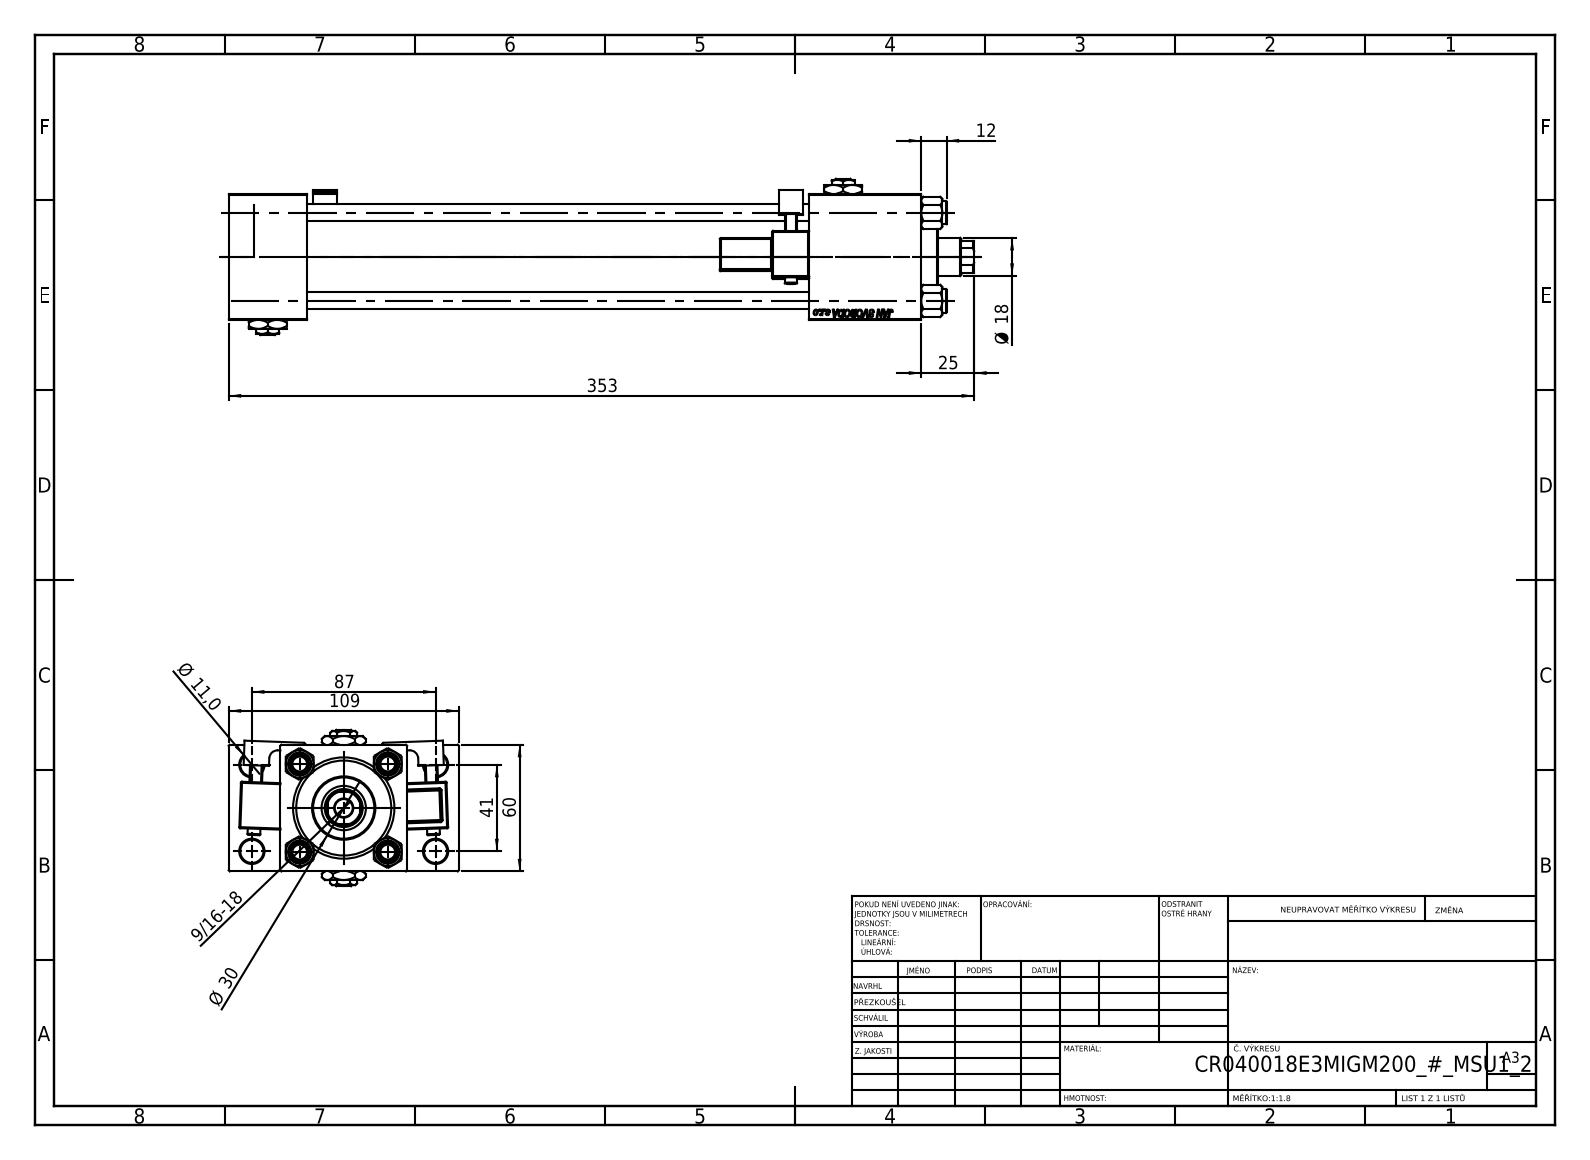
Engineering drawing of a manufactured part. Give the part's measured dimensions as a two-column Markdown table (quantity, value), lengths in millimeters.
| quantity | value |
| --- | --- |
| part name | V215CR_MSU; Zatka_pro_OIL_PORT; V215CR_E_Body; V215CR_VCP_E (+3 more) |
| STEP written by | SolidWorks 2019 (CONFIG_CONTROL_DESIGN) |
| units | millimeters |
| bodies | 15 solids, 1385 faces (602 planar, 153 cylindrical, 630 other) |
| overall size | 353 × 109 × 74 |
| volume | 695 320 mm³ |
| surface area | 216 006 mm² |
| round holes (diameter × count) | 8 × 4, 11 × 4, 7 × 3, 16.66 × 3, 24 × 3, 8.5 × 1, 18 × 1, 21 × 1, 31 × 1, 40 × 1, 45 × 1 |
| round bosses / shafts (diameter × count) | 11 × 4, 6 × 2, 46 × 1, 30 × 1 |
| partial cylindrical surfaces (radius × count) | 0.5 × 48, 1 × 2, 2.5 × 2, 4 × 2, 8.5 × 1 |
| main face-to-face distances | 60, 37, 24.5, 84.5, 53, 328, 291, 275, 238, 24.3 |
| hole center spacings | 22.65, 29.49, 41.7, 47.15, 48.09, 64.35, 76.49, 41 |
